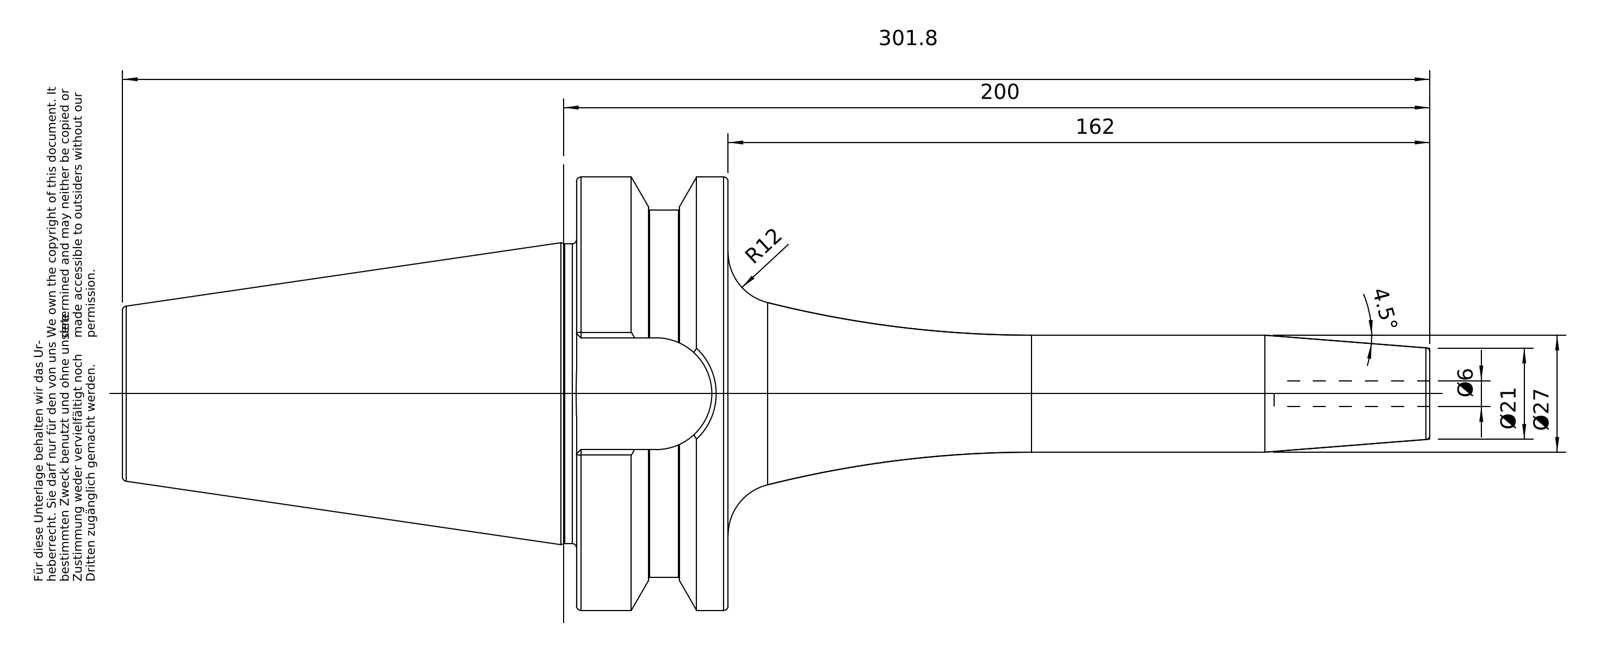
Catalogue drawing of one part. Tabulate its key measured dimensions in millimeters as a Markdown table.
| quantity | value |
| --- | --- |
| part name | 50-646-06 |
| STEP written by | PRO/ENGINEER BY PARAMETRIC TECHNOLOGY CORPORATION, 2010430 (CONFIG_CONTROL_DESIGN) |
| units | millimeters |
| bodies | 1 solid, 98 faces (26 planar, 22 cylindrical, 50 other) |
| overall size | 301.8 × 99.97 × 99.97 |
| volume | 581 821 mm³ |
| surface area | 65 721 mm² |
| round holes (diameter × count) | 6 × 1, 20.75 × 1, 25.02 × 1, 25.7 × 1 |
| round bosses / shafts (diameter × count) | 99.97 × 1, 84.75 × 1, 69.15 × 1, 27 × 1, 24.01 × 1 |
| partial cylindrical surfaces (radius × count) | 12.9 × 1 |
| main face-to-face distances | 35, 70.4, 104.8, 139.8, 25.8, 301.8, 197, 162, 48, 56.8 |
